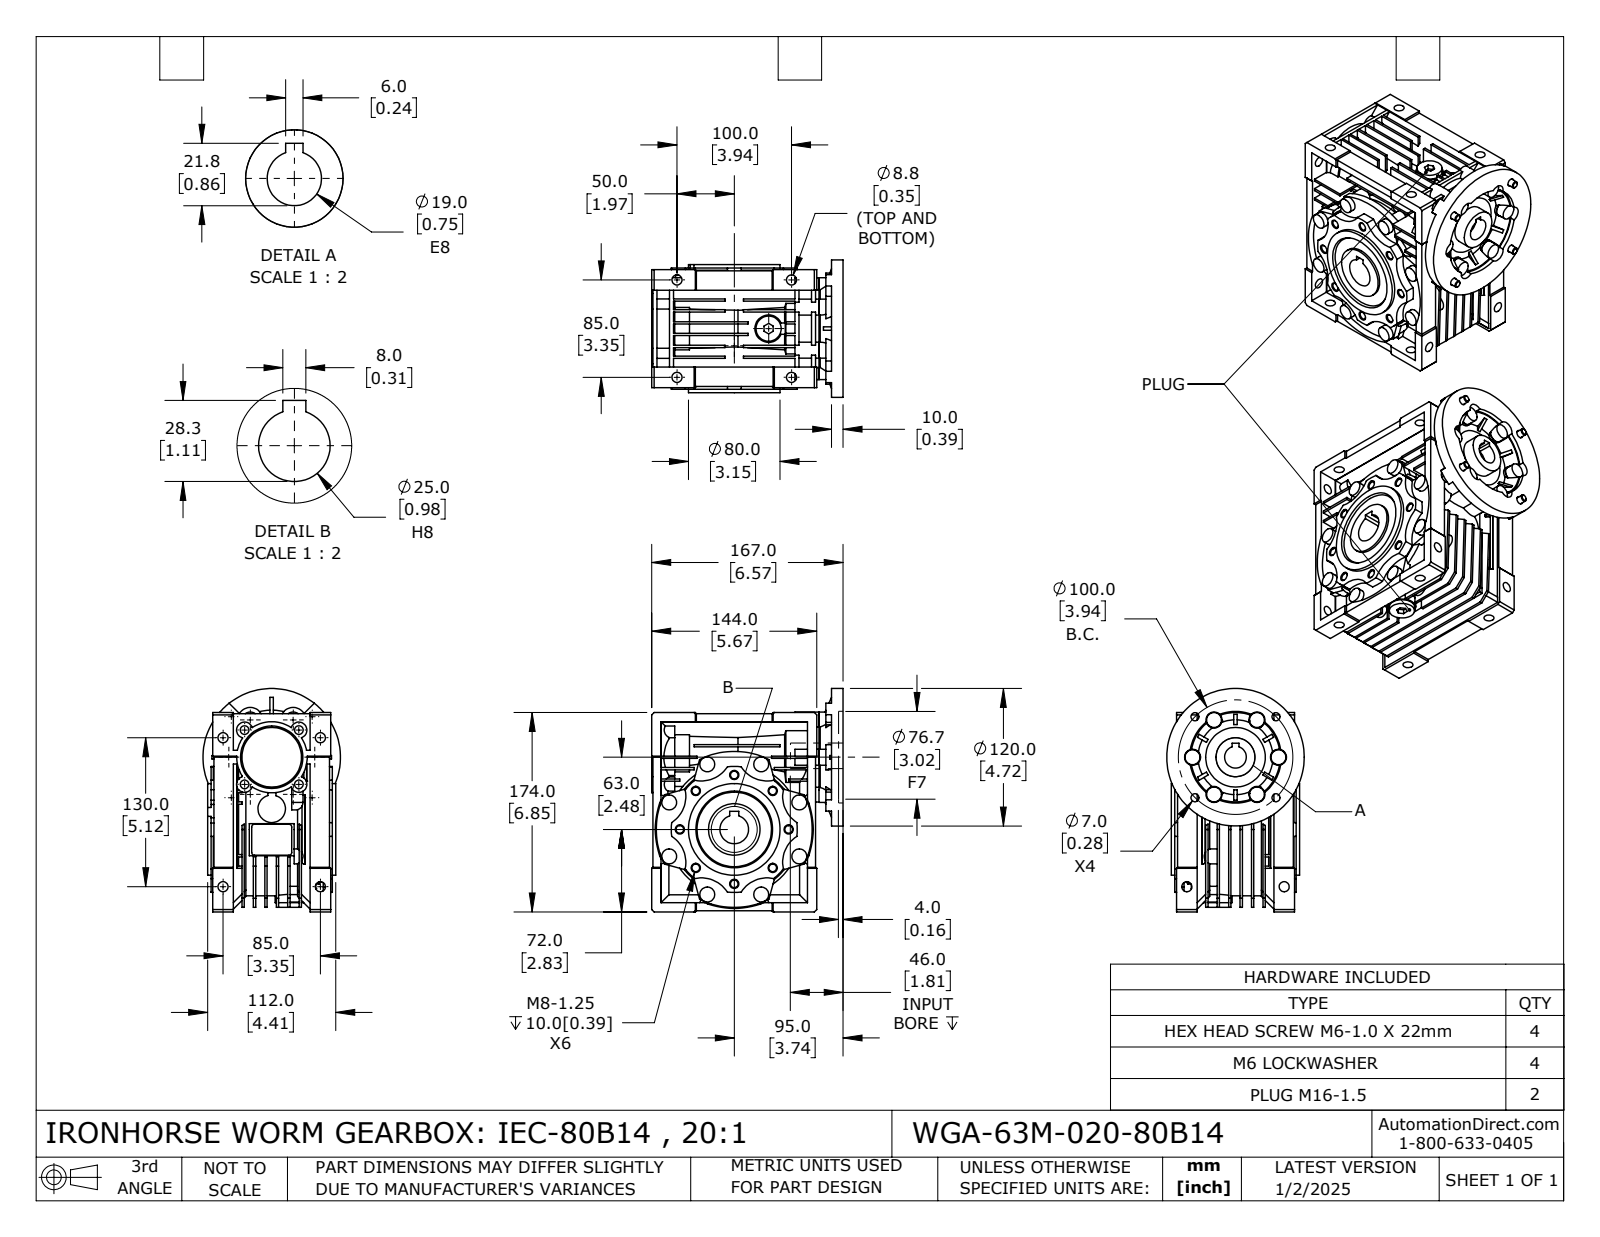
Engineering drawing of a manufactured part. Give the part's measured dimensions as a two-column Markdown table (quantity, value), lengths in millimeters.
| quantity | value |
| --- | --- |
| part name | WGA-63M-020-80B14 |
| STEP written by | SolidWorks 2024 (CONFIG_CONTROL_DESIGN) |
| units | millimeters |
| bodies | 16 solids, 1442 faces (853 planar, 413 cylindrical, 176 other) |
| overall size | 195 × 172.5 × 120 |
| volume | 1 847 000 mm³ |
| surface area | 350 234 mm² |
| round holes (diameter × count) | 6.65 × 8, 8.78 × 8, 6.1 × 4, 7 × 4, 7.56 × 4, 14.5 × 2, 19 × 1, 20 × 1, 25 × 1, 34 × 1, 37 × 1, 45 × 1 |
| round bosses / shafts (diameter × count) | 13 × 14, 14 × 6, 12.2 × 4, 6 × 4, 24 × 3, 22 × 2, 15.8 × 2, 13.7 × 2 |
| partial cylindrical surfaces (radius × count) | 7 × 10, 27 × 8, 6.98 × 6, 11 × 6, 2.5 × 4, 8.35 × 1, 29.5 × 1, 30.5 × 1 |
| main face-to-face distances | 10, 8, 20, 2, 30, 18, 12, 7, 40, 1 |
| hole center spacings | 36.36, 47.5, 60.19, 67.18, 87.77, 16.5, 33.5, 47.38 |
